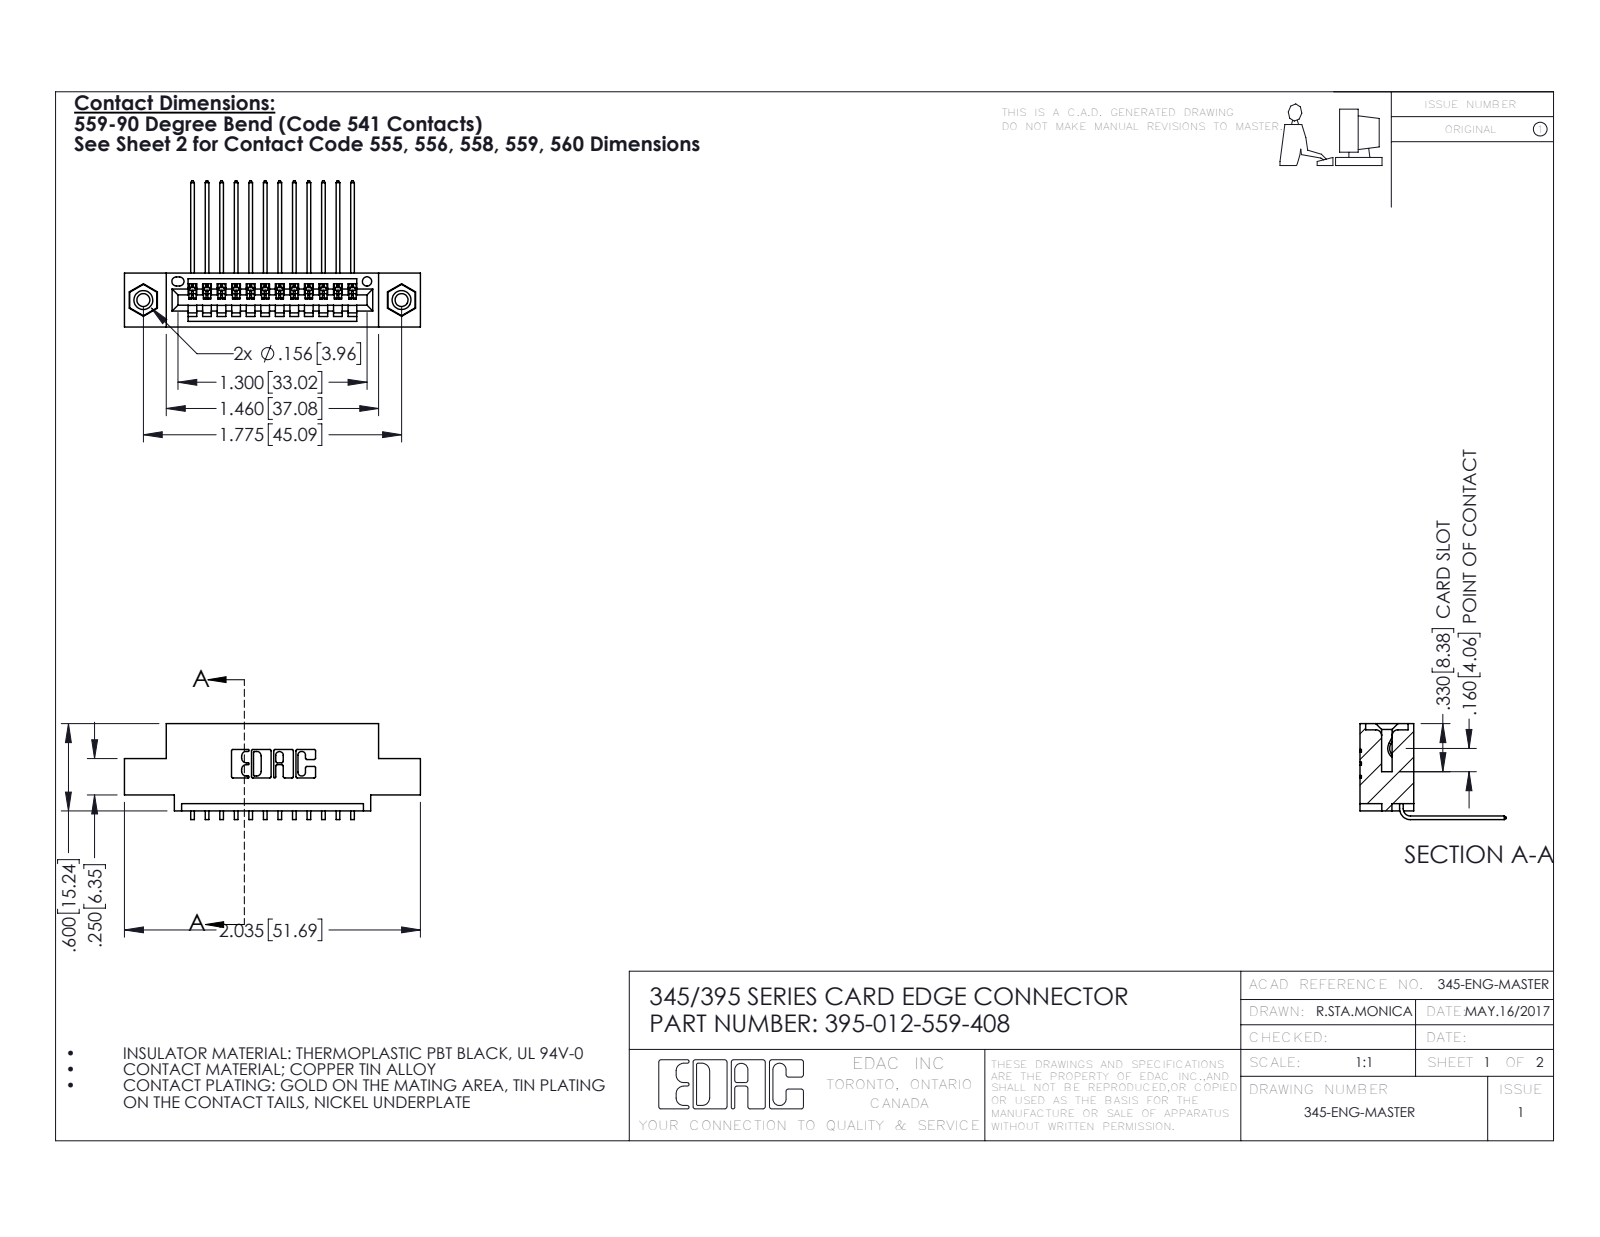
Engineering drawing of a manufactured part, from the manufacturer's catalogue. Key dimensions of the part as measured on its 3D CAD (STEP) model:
Part name (STEP PRODUCT): 395-012-559-408; 345-250-001_345-250-003-102; 345 Part_0.110 Offset - 0.156 Dia-TI; 345-292-001_558 559 Tail - 1
STEP written by: SolidWorks 2016 (CONFIG_CONTROL_DESIGN)
Units: inches
Bodies: 15 solids, 910 faces (620 planar, 274 cylindrical, 16 other)
Overall size (bounding box): 2.035 × 1.005 × 0.659
Volume: 0.282 in³ · Surface area: 9.413 in²
Round holes (diameter × count): ⌀0.089 ×2, ⌀0.125 ×2, ⌀0.156 ×2, ⌀0.064 ×1
Round bosses / shafts (diameter × count): ⌀0.155 ×2
Partial cylindrical surfaces — rounded edges, fillets, slot ends (radius × count): R0.006 ×24, R0.01 ×22, R0.007 ×6, R0.031 ×6, R0.026 ×3, R0.031 ×2, R0.04 ×2, R0.014 ×1
Main face-to-face distances: 0.2, 0.072, 0.298, 0.37, 0.098, 0.272, 0.025, 0.1, 0.16, 0.3
Hole centre spacings: 0.27, 1.543, 1.775
